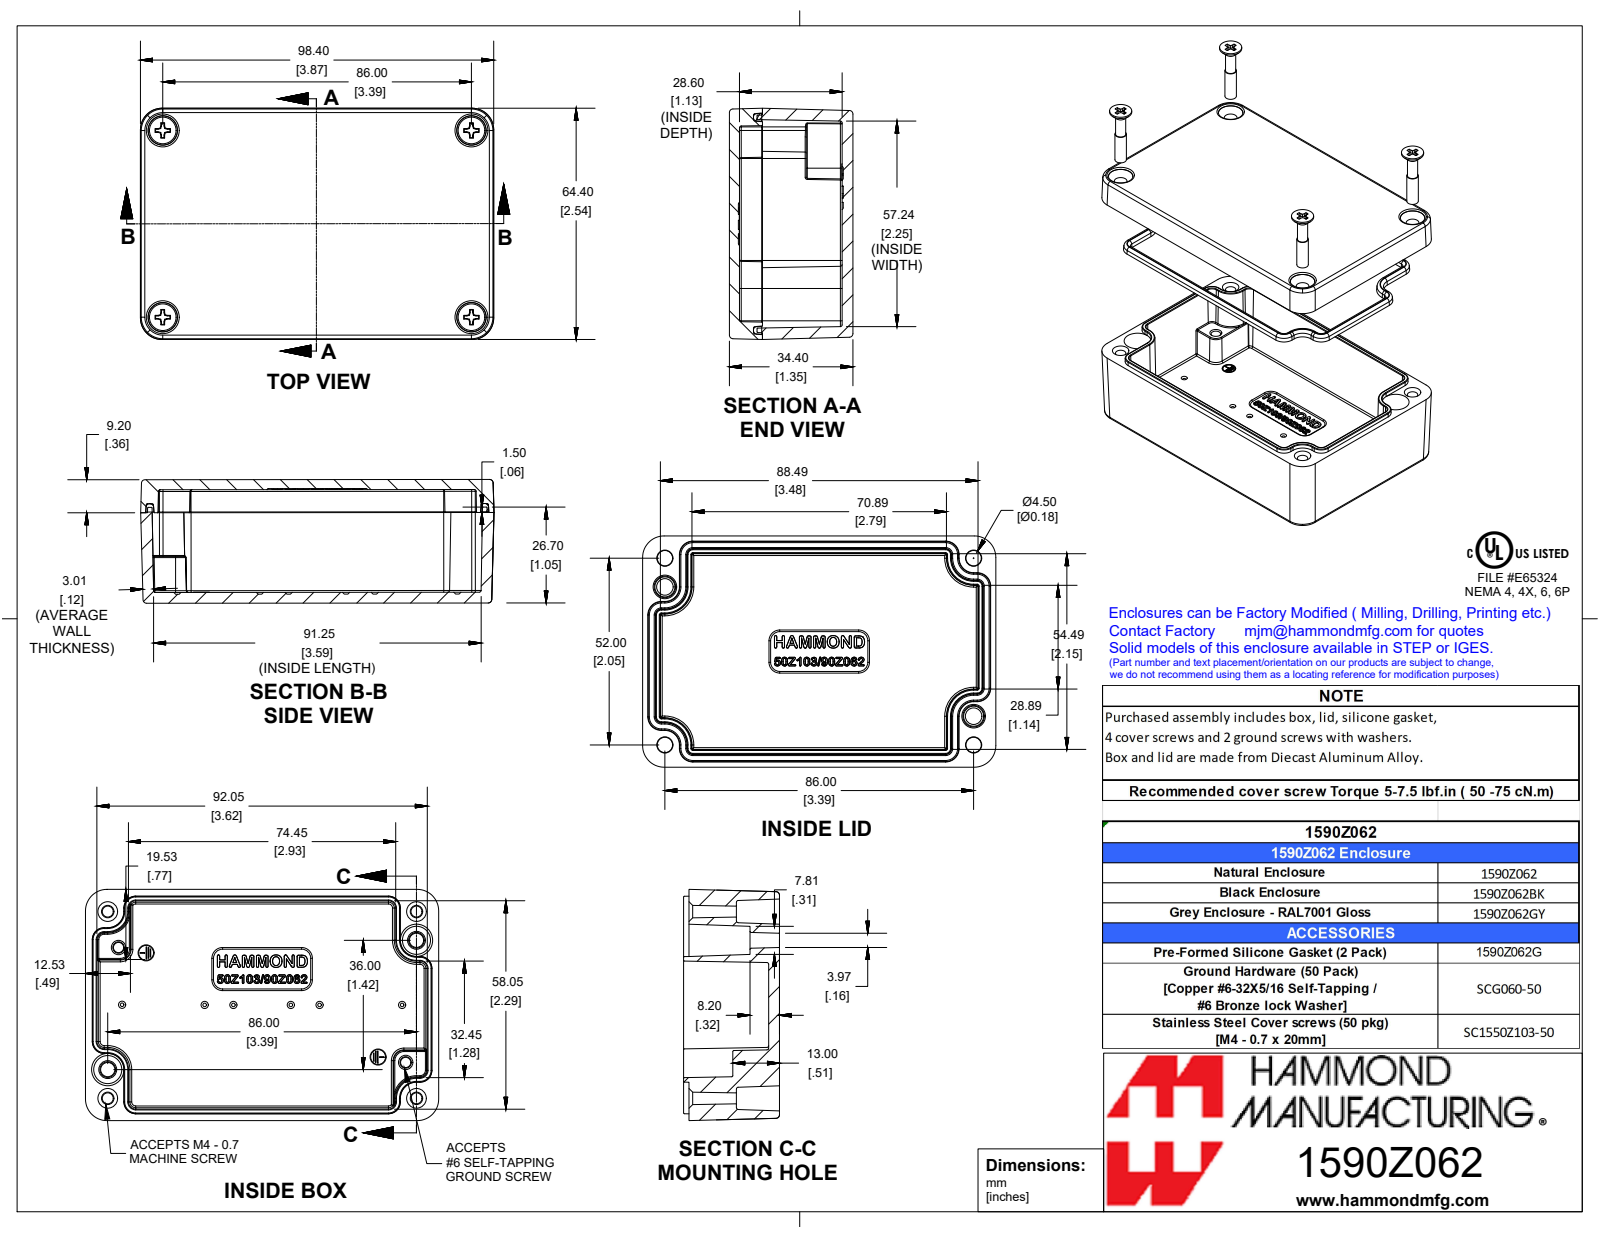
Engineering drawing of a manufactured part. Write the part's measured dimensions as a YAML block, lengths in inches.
part_name: "1590Z062BK"
step_written_by: "SolidWorks 2019 (CONFIG_CONTROL_DESIGN)"
units: inches
bodies: {solids: 7, faces: 1387, planar: 421, cylindrical: 164, other: 802}
overall_size: [3.874, 2.535, 1.354]
volume: 4.575
surface_area: 81.04
round_bosses_or_shafts:
  - {diameter: 0.15, count: 4}
  - {diameter: 0.135, count: 4}
partial_cylinders:
  - {radius: 0.008, count: 40}
  - {radius: 0.012, count: 32}
  - {radius: 0.02, count: 30}
  - {radius: 0.039, count: 28}
  - {radius: 0.236, count: 8}
face_to_face_distances: [1.354, 1.236, 0.118, 1.244, 1.126, 0.11, 0.252, 0.992, 0.874, 0.362]
